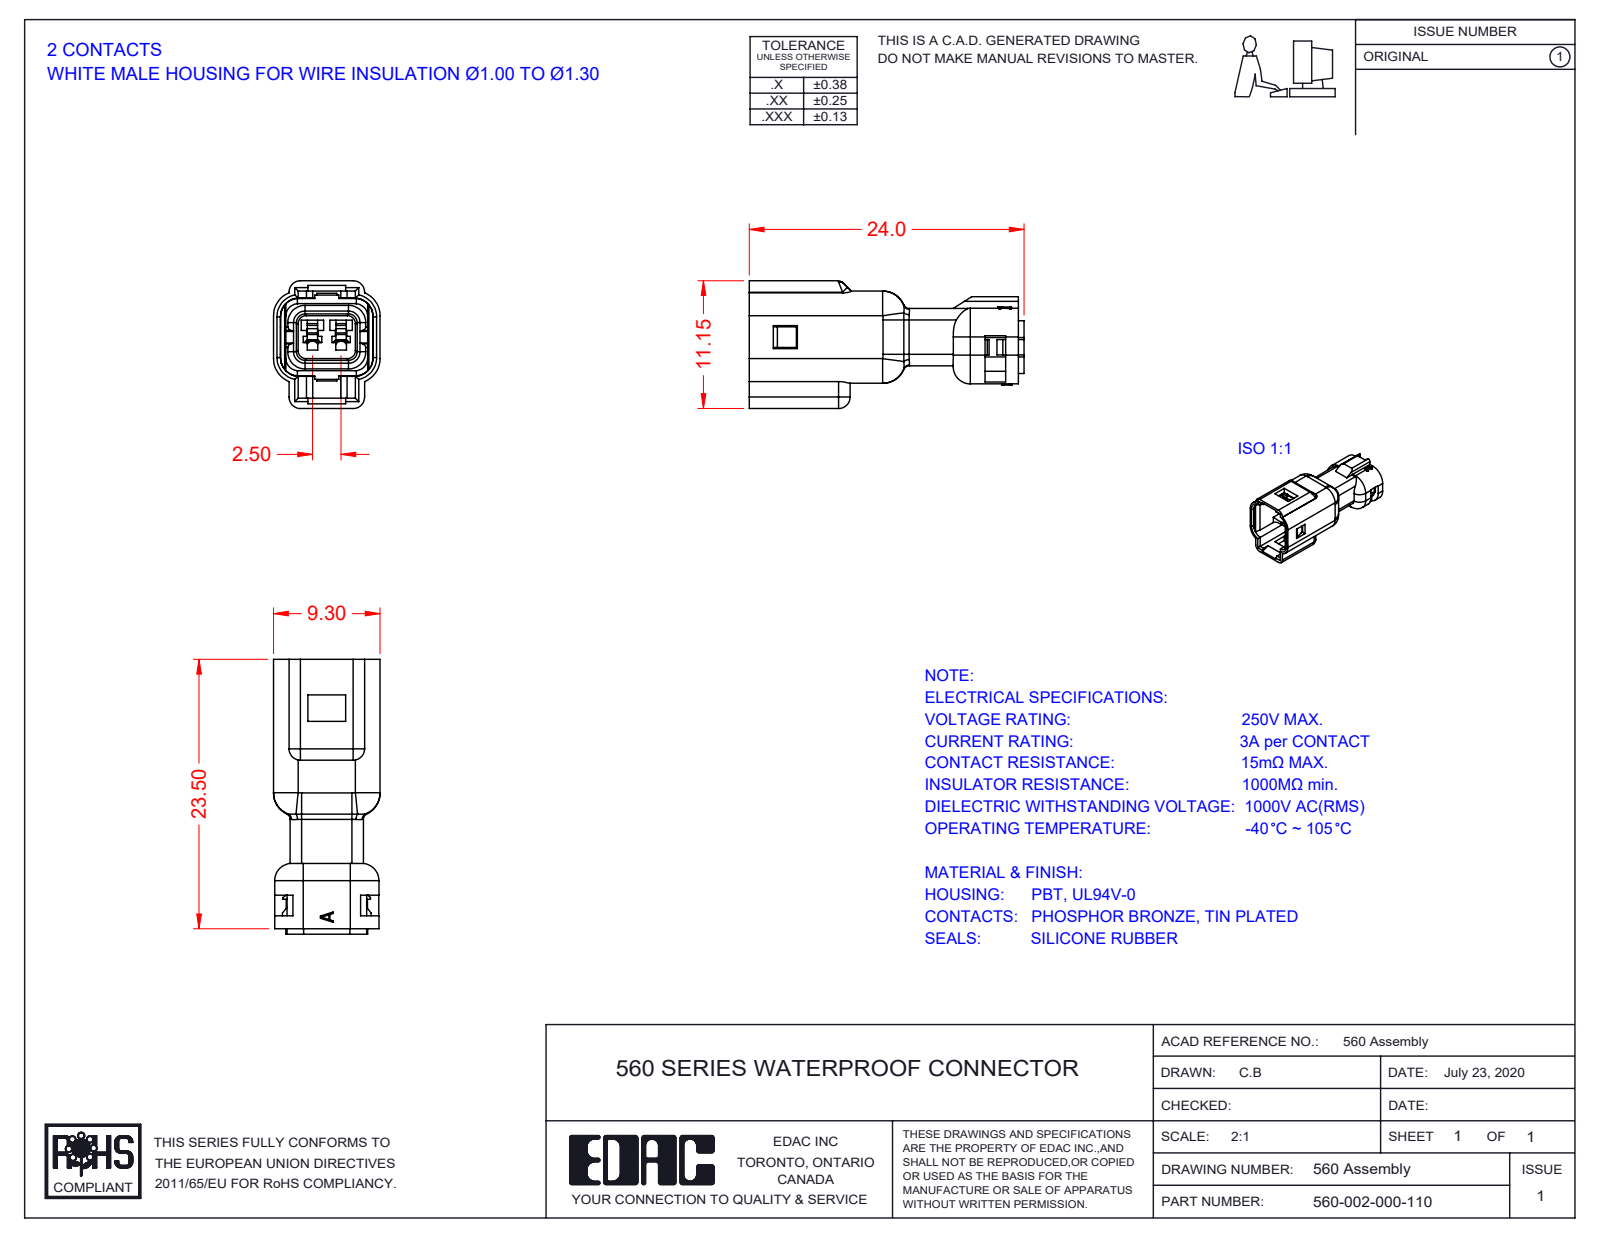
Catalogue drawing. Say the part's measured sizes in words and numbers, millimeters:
The part is named "REAR-GASKET-2POS_YELLOW; FACIAL-SEAL-2POS; MALE-HOUSING-2POS_WHITE; INTERNAL-WIRE-SEAL-2POS (+2 more)". Its 3-D file was written by "SolidWorks 2020 (CONFIG_CONTROL_DESIGN)". It is 5 solids with 895 faces: 495 planar, 209 cylindrical and 191 other. Overall it measures 23.98 by 11.15 by 9.3 millimeters. Its volume is 900 cubic millimeters and its surface area 2 421 square millimeters. Round holes: 2 of diameter 1.5. Partial cylindrical surfaces (rounded edges, fillets, slot ends): 25 of radius 1, 16 of radius 0.25, 13 of radius 0.35, 12 of radius 1.2, 9 of radius 0.15, 8 of radius 1.5, 8 of radius 1.65, 5 of radius 0.5. The main face-to-face distances are 0.6, 0.9, 1.07, 8.7, 7.6, 8.1, 2.15, 7.15, 0.8, 4.7. The hole center spacings are 2.5.
